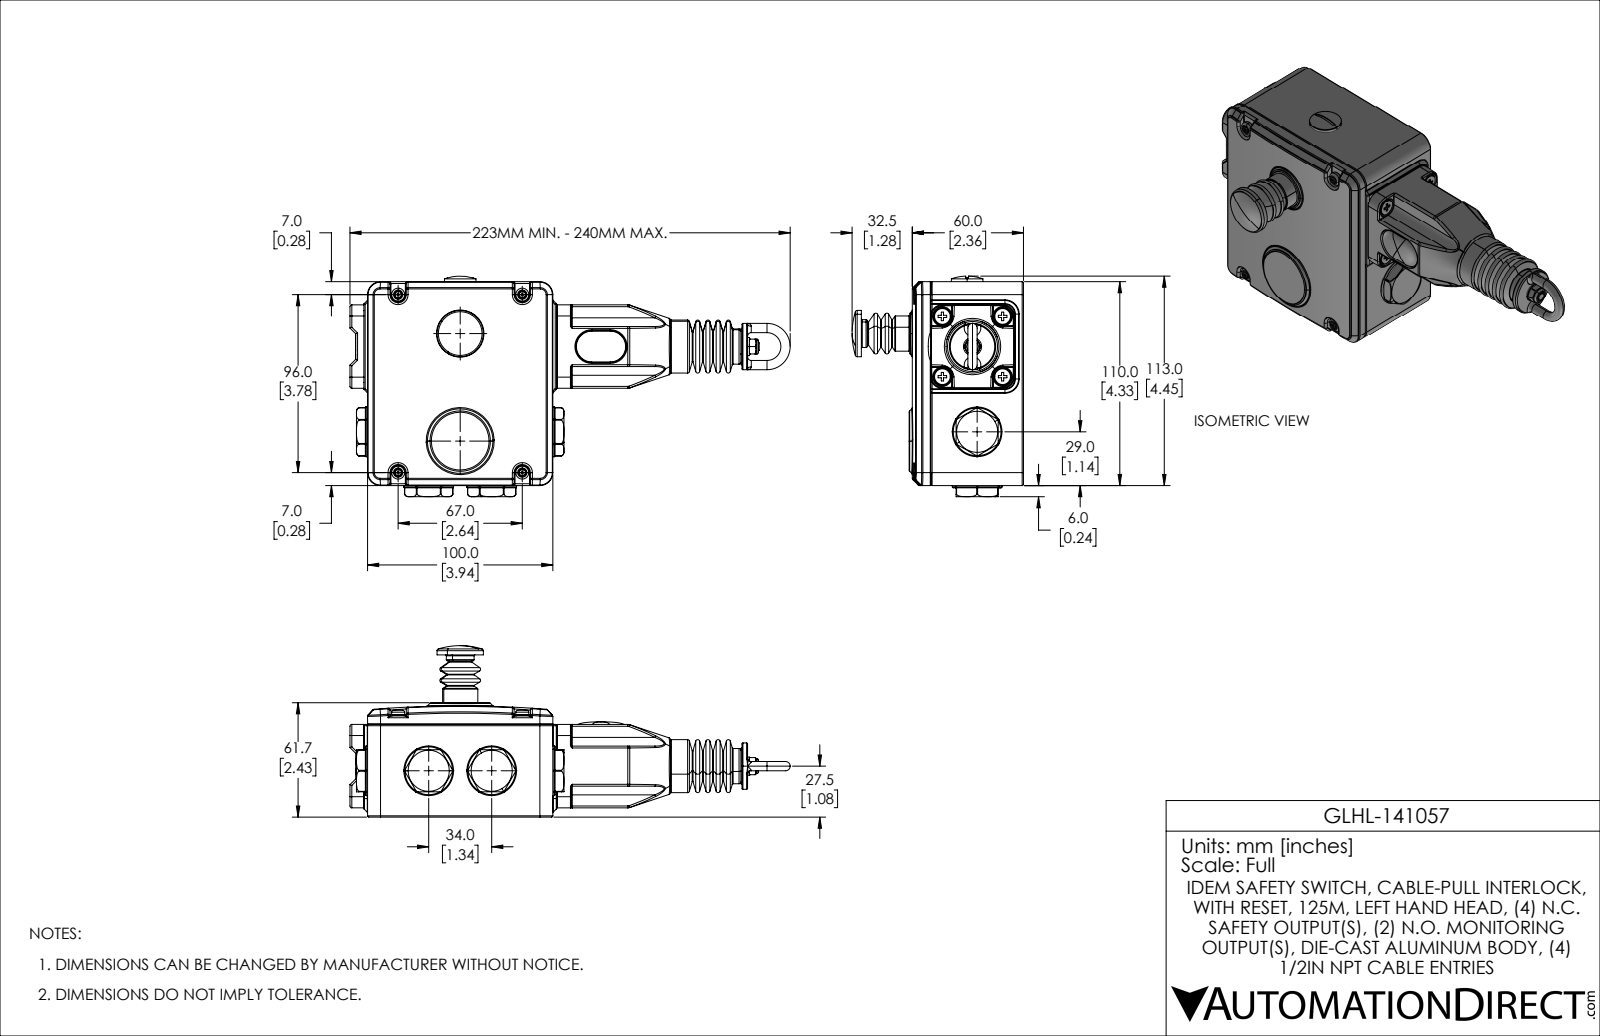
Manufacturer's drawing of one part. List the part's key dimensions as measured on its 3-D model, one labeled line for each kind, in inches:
Part name (STEP PRODUCT): GLHL-141057
STEP written by: SolidWorks 2021 (AUTOMOTIVE_DESIGN)
Units: inches
Bodies: 30 solids, 3775 faces (1036 planar, 1206 cylindrical, 1533 other)
Overall size (bounding box): 9.354 × 4.685 × 3.642
Volume: 17.53 in³ · Surface area: 261.2 in²
Round holes (diameter × count): ⌀0.197 ×10, ⌀0.209 ×9, ⌀0.374 ×7, ⌀0.354 ×5, ⌀0.13 ×4, ⌀0.157 ×4, ⌀0.189 ×4, ⌀0.213 ×4, ⌀0.228 ×4, ⌀0.118 ×3, ⌀0.173 ×3, ⌀0.504 ×3
Round bosses / shafts (diameter × count): ⌀0.335 ×7, ⌀0.236 ×7, ⌀0.173 ×7, ⌀0.197 ×6, ⌀0.276 ×5, ⌀0.138 ×4, ⌀0.051 ×4, ⌀1.055 ×3
Partial cylindrical surfaces — rounded edges, fillets, slot ends (radius × count): R0.02 ×226, R0.039 ×153, R0.028 ×72, R0.008 ×64, R0.012 ×20, R0.006 ×14, R0.236 ×12, R0.004 ×8
Main face-to-face distances: 0.138, 2.157, 2.043, 0.114, 4.331, 0.055, 0.157, 4.016, 3.878, 0.079
Hole centre spacings: 1.28, 1.281, 0.374, 0.905, 1.891, 1.913, 3.012, 3.489
